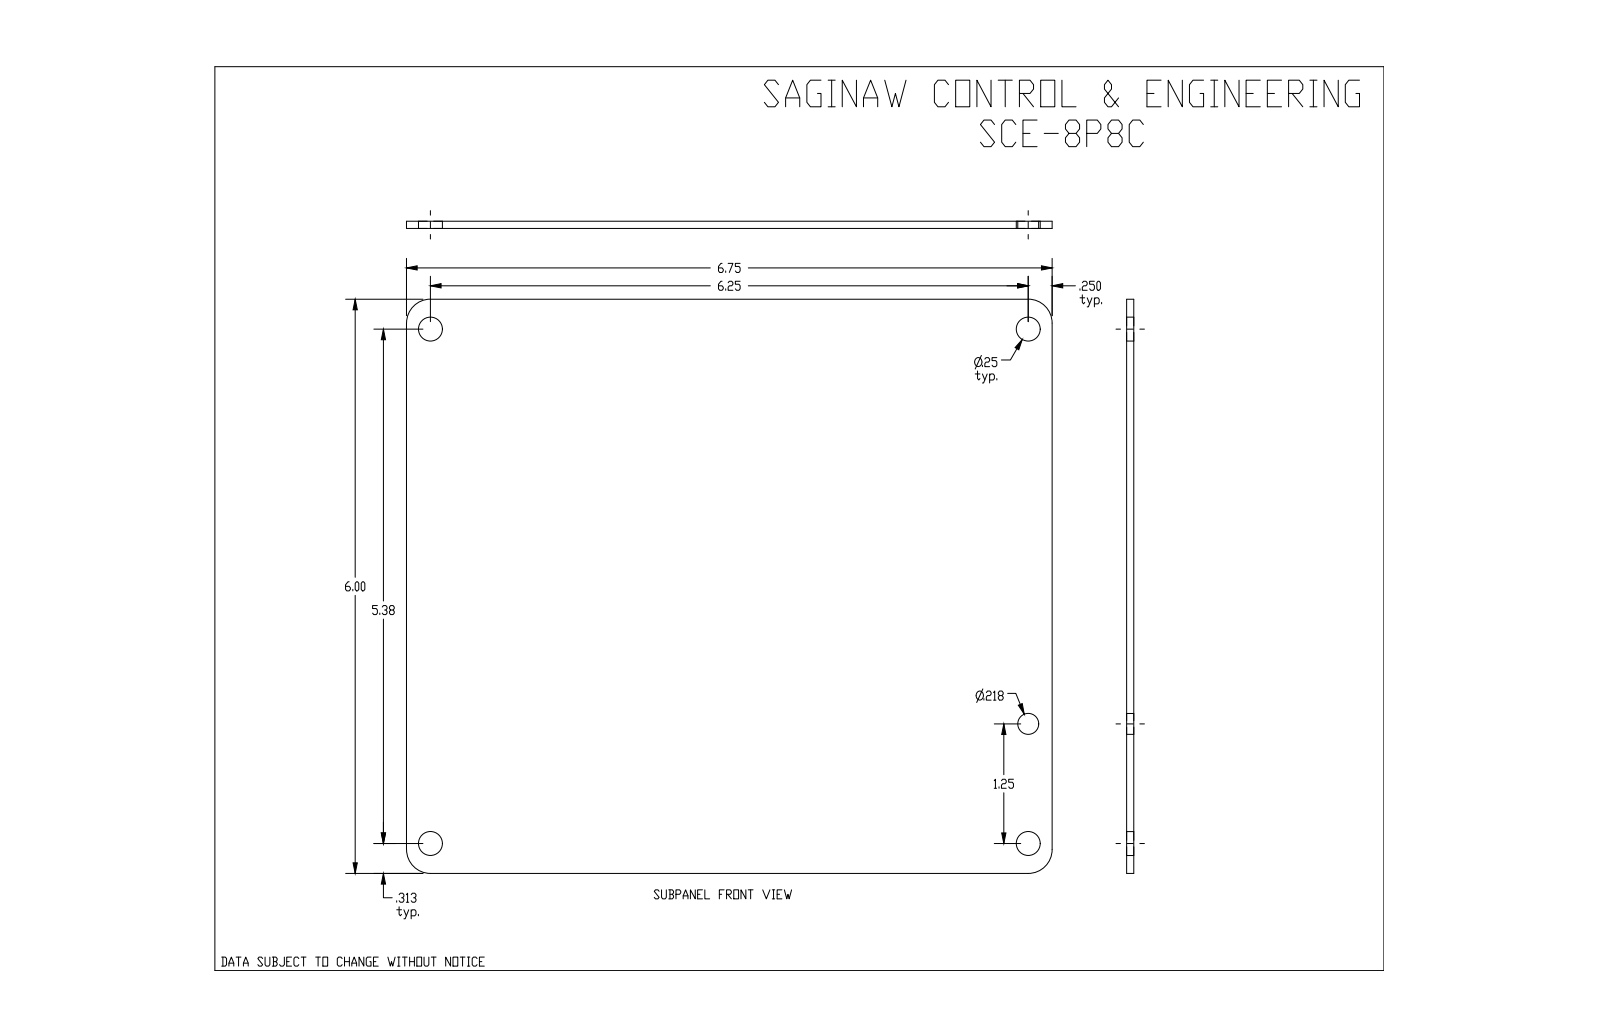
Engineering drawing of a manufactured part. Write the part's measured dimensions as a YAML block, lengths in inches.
part_name: "SCE-8P8C"
step_written_by: "SolidWorks 2019 (CONFIG_CONTROL_DESIGN)"
units: inches
bodies: {solids: 1, faces: 15, planar: 6, cylindrical: 9, other: 0}
overall_size: [6.75, 6, 0.075]
volume: 3.016
surface_area: 82.59
round_holes:
  - {diameter: 0.25, count: 4}
  - {diameter: 0.218, count: 1}
partial_cylinders:
  - {radius: 0.25, count: 4}
face_to_face_distances: [0.075, 6, 6.75]
hole_center_spacings: [5.375, 6.25, 8.244, 1.25, 4.125, 6.374, 7.489]
